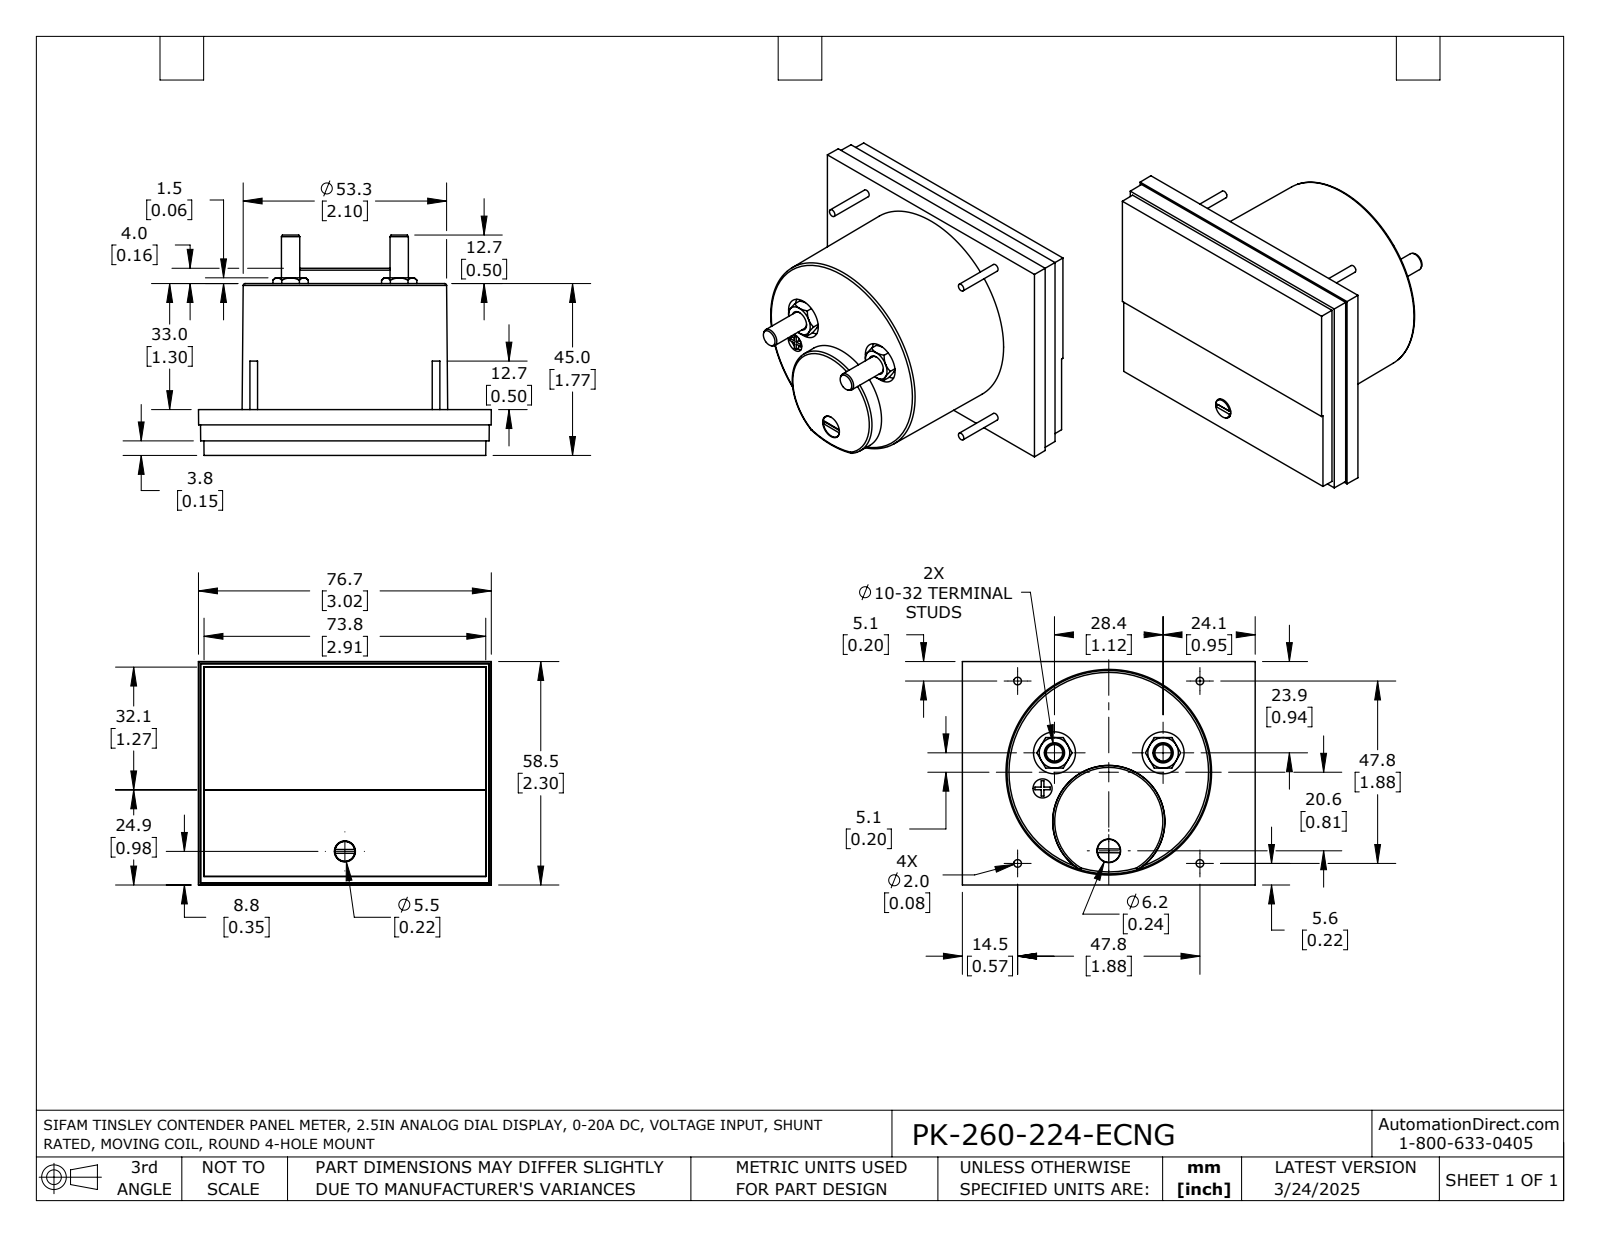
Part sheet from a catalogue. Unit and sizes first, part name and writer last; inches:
Units: inches
Overall size (bounding box): 3.02 × 2.303 × 2.272
Round holes (diameter × count): ⌀0.197 ×3, ⌀0.433 ×2, ⌀0.209 ×1, ⌀0.217 ×1, ⌀0.244 ×1
Round bosses / shafts (diameter × count): ⌀0.079 ×4, ⌀0.189 ×2, ⌀0.236 ×1, ⌀0.205 ×1
Partial cylindrical surfaces — rounded edges, fillets, slot ends (radius × count): R0.033 ×1
Main face-to-face distances: 0.02, 0.472, 0.13, 0.322, 0.15, 0.453, 0.057, 0.077, 0.396, 0.073
Hole centre spacings: 1.155, 1.16, 0.387, 0.938, 0.942, 1.12, 1.295
Volume: 7.657 in³ · Surface area: 36.55 in²
Bodies: 1 solid, 192 faces (95 planar, 37 cylindrical, 60 other)
Part name (STEP PRODUCT): PK-260-224-ECNG
STEP written by: SolidWorks 2021 (AUTOMOTIVE_DESIGN)
